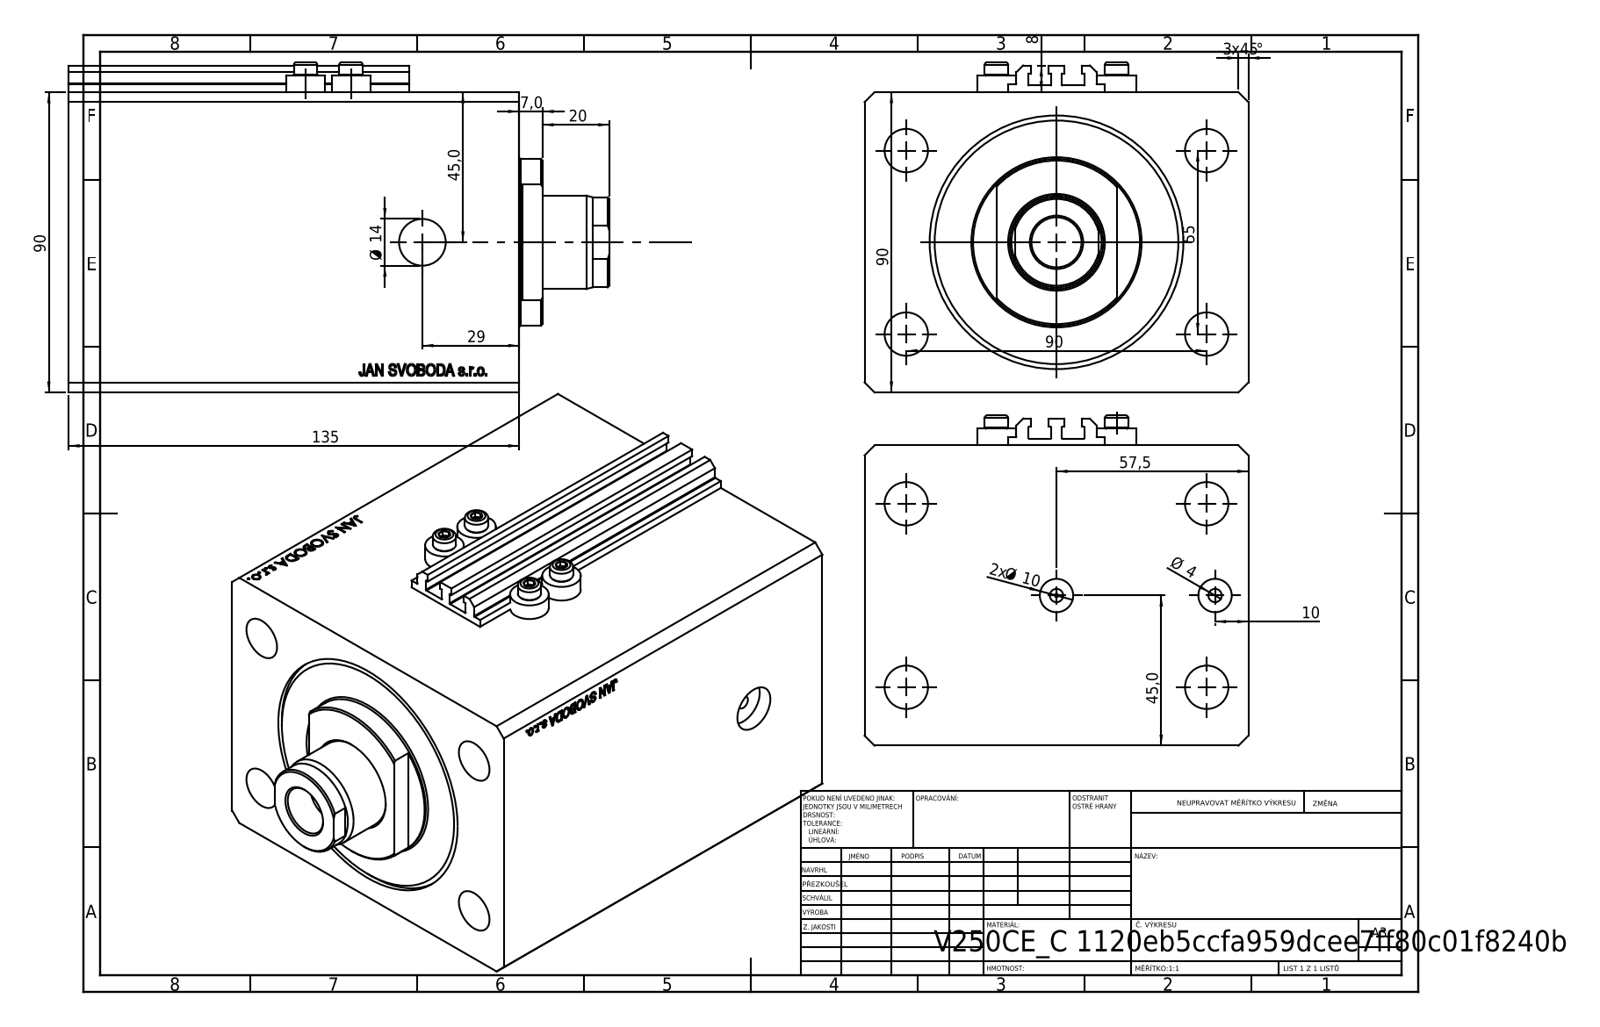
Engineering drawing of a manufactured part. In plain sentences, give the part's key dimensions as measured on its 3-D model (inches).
The part is named "ALLEN BOLT V250CE; V250CE_C_vnitrni cast pro vysunuti; V250CE_C; V250CE_C_VCP". Its 3-D file was written by "SolidWorks 2019 (CONFIG_CONTROL_DESIGN)". It is 8 solids with 1027 faces: 501 planar, 84 cylindrical and 442 other. Overall it measures 6.378 by 4.528 by 3.898 inches. Its volume is 75.18 cubic inches and its surface area 268.8 square inches. Round holes: 7 of diameter 0.157, 4 of diameter 0.512, 2 of diameter 0.394, 2 of diameter 0.551, 1 of diameter 0.049, 1 of diameter 0.591, 1 of diameter 1.102, 1 of diameter 2.48, 1 of diameter 2.992. Round bosses or shafts: 4 of diameter 0.457, 4 of diameter 0.276, 1 of diameter 1.969. Partial cylindrical surfaces (rounded edges, fillets, slot ends): 10 of radius 0.008, 1 of radius 0.531. The main face-to-face distances are 3.543, 4.528, 5.315, 0.709, 4.606, 4.843, 4.134, 0.472, 1.969, 2.165. The hole center spacings are 2.076, 0.535, 1.087, 1.417, 1.515, 2.165, 3.543, 3.799.
